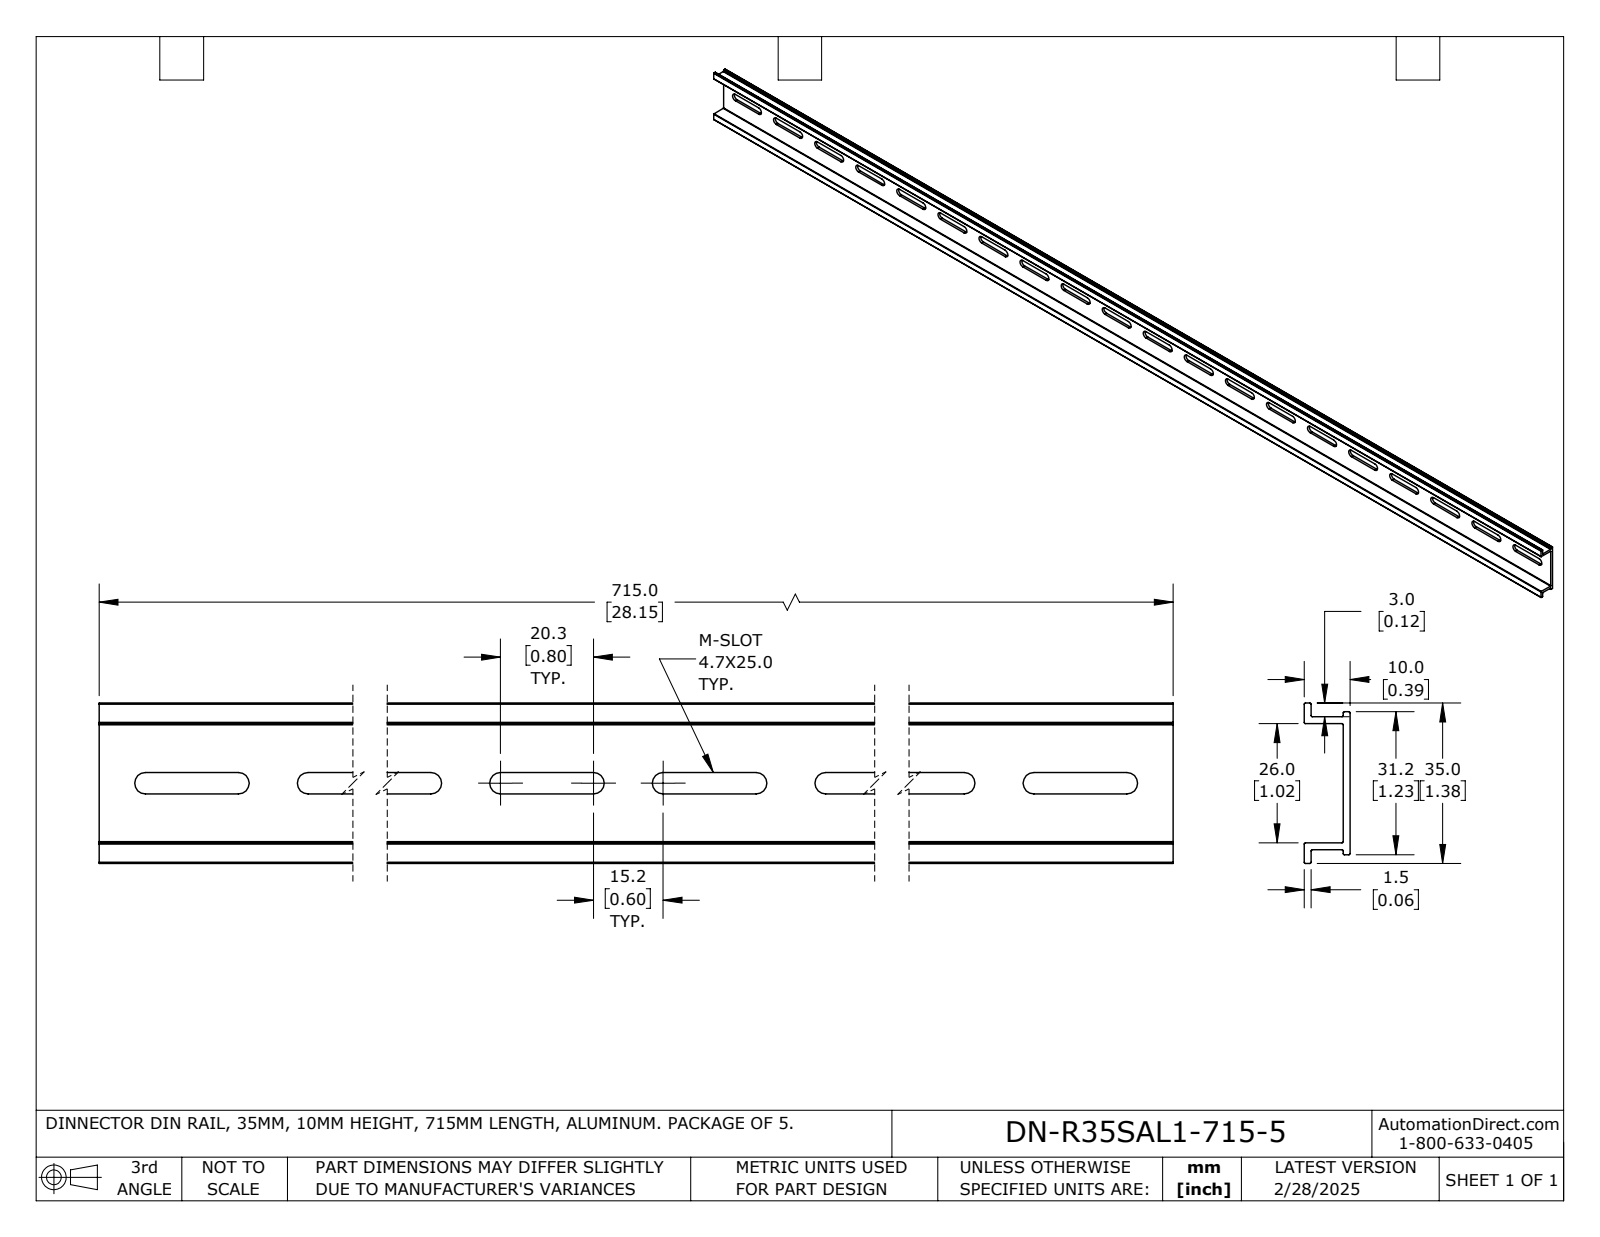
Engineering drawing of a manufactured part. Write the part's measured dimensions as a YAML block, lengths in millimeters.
part_name: "DN-R35SAL1-715-5_Default"
step_written_by: "SolidWorks 2024 (CONFIG_CONTROL_DESIGN)"
units: millimeters
bodies: {solids: 1, faces: 114, planar: 58, cylindrical: 56, other: 0}
overall_size: [715, 35, 10]
volume: 54703
surface_area: 75648
partial_cylinders:
  - {radius: 2.35, count: 40}
  - {radius: 0.27, count: 16}
face_to_face_distances: [1.5, 27.5, 8.5, 26, 10, 29, 7, 1.1, 2.6, 28.6]
